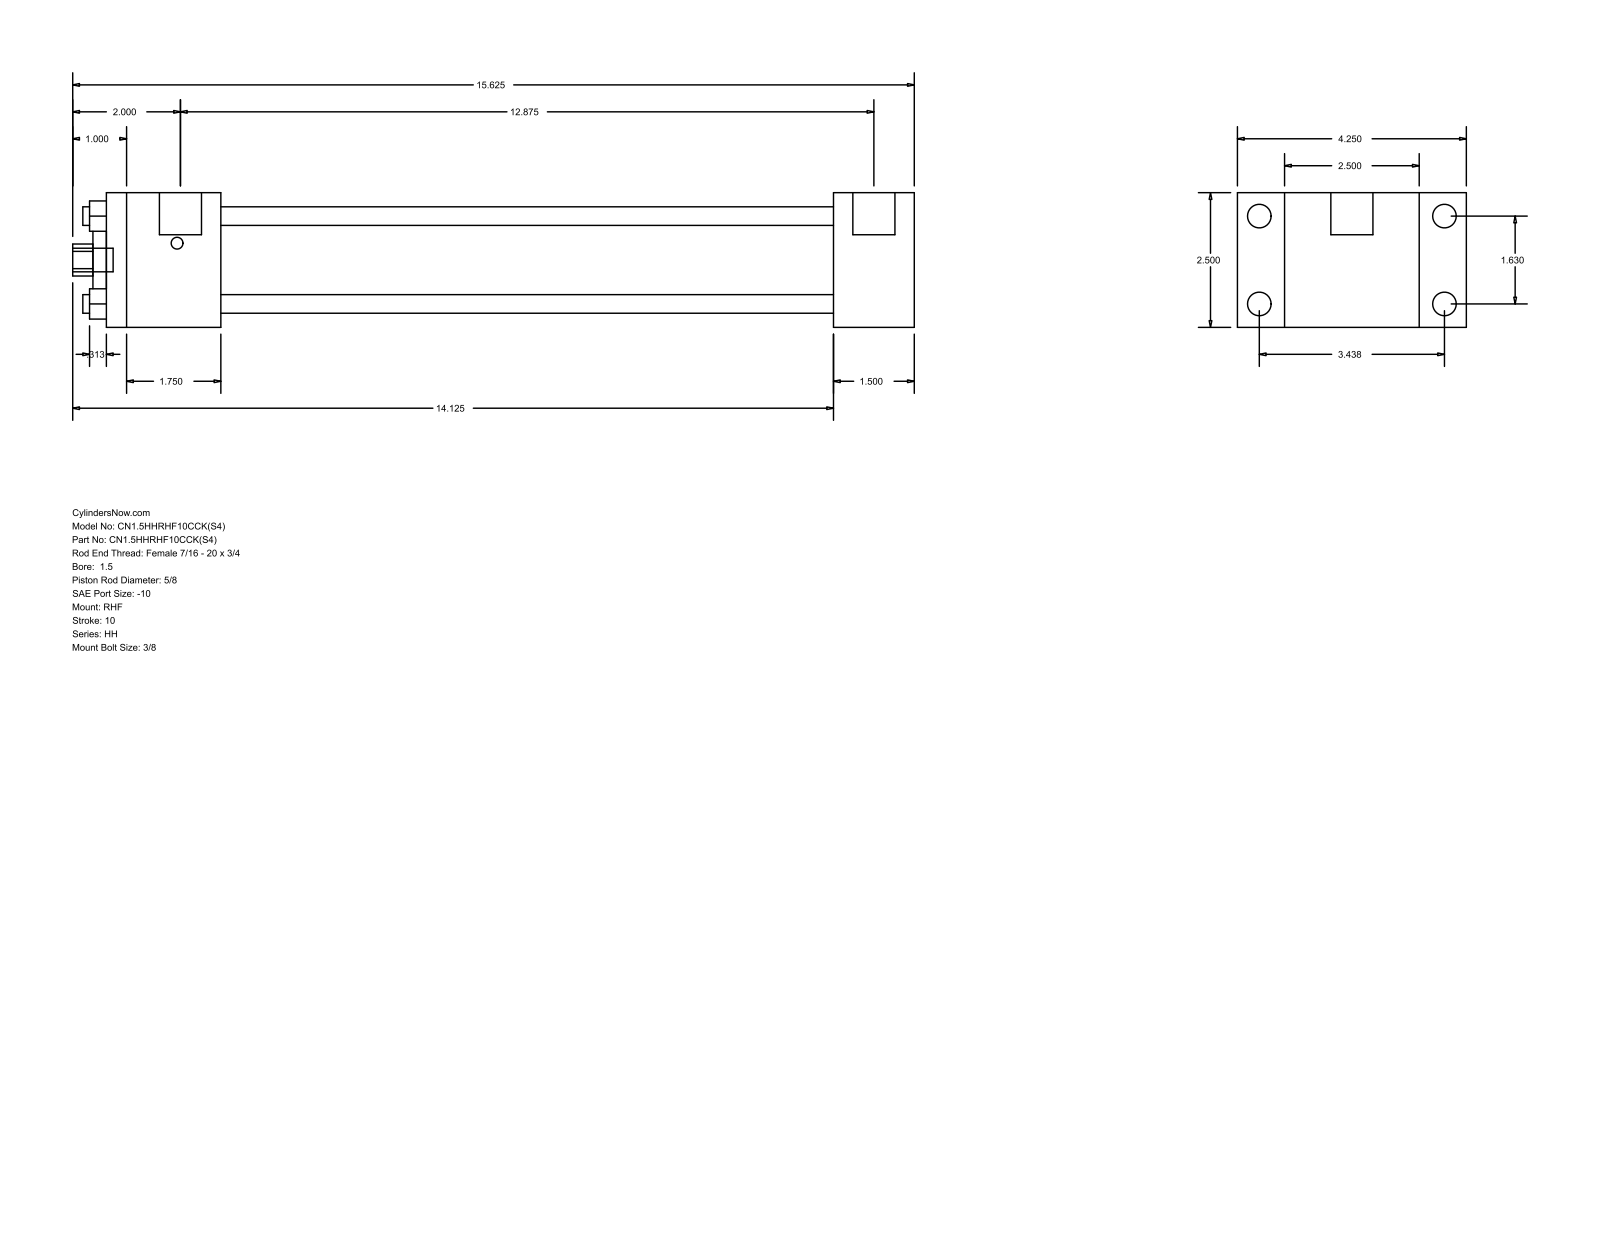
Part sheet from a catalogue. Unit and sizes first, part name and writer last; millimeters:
Units: millimetres
Overall size (bounding box): 396.88 × 107.95 × 63.5
Round holes (diameter × count): ⌀8.76 ×4, ⌀15.88 ×1, ⌀28.57 ×1, ⌀44.45 ×1
Round bosses / shafts (diameter × count): ⌀11.13 ×4, ⌀5.56 ×4, ⌀19.84 ×2, ⌀11.11 ×1
Partial cylindrical surfaces — rounded edges, fillets, slot ends (radius × count): R7.54 ×1
Main face-to-face distances: 63.5, 22.23, 85.73, 38.11, 342.89, 381, 107.96, 53.97, 288.92, 327.03
Hole centre spacings: 29.27, 41.4, 58.55
Bodies: 0 solids, 88 faces (60 planar, 28 cylindrical, 0 other)
Part name (STEP PRODUCT): HH_RHF__0150_0.625
STEP written by: GSSL Pune (CONFIG_CONTROL_DESIGN)
